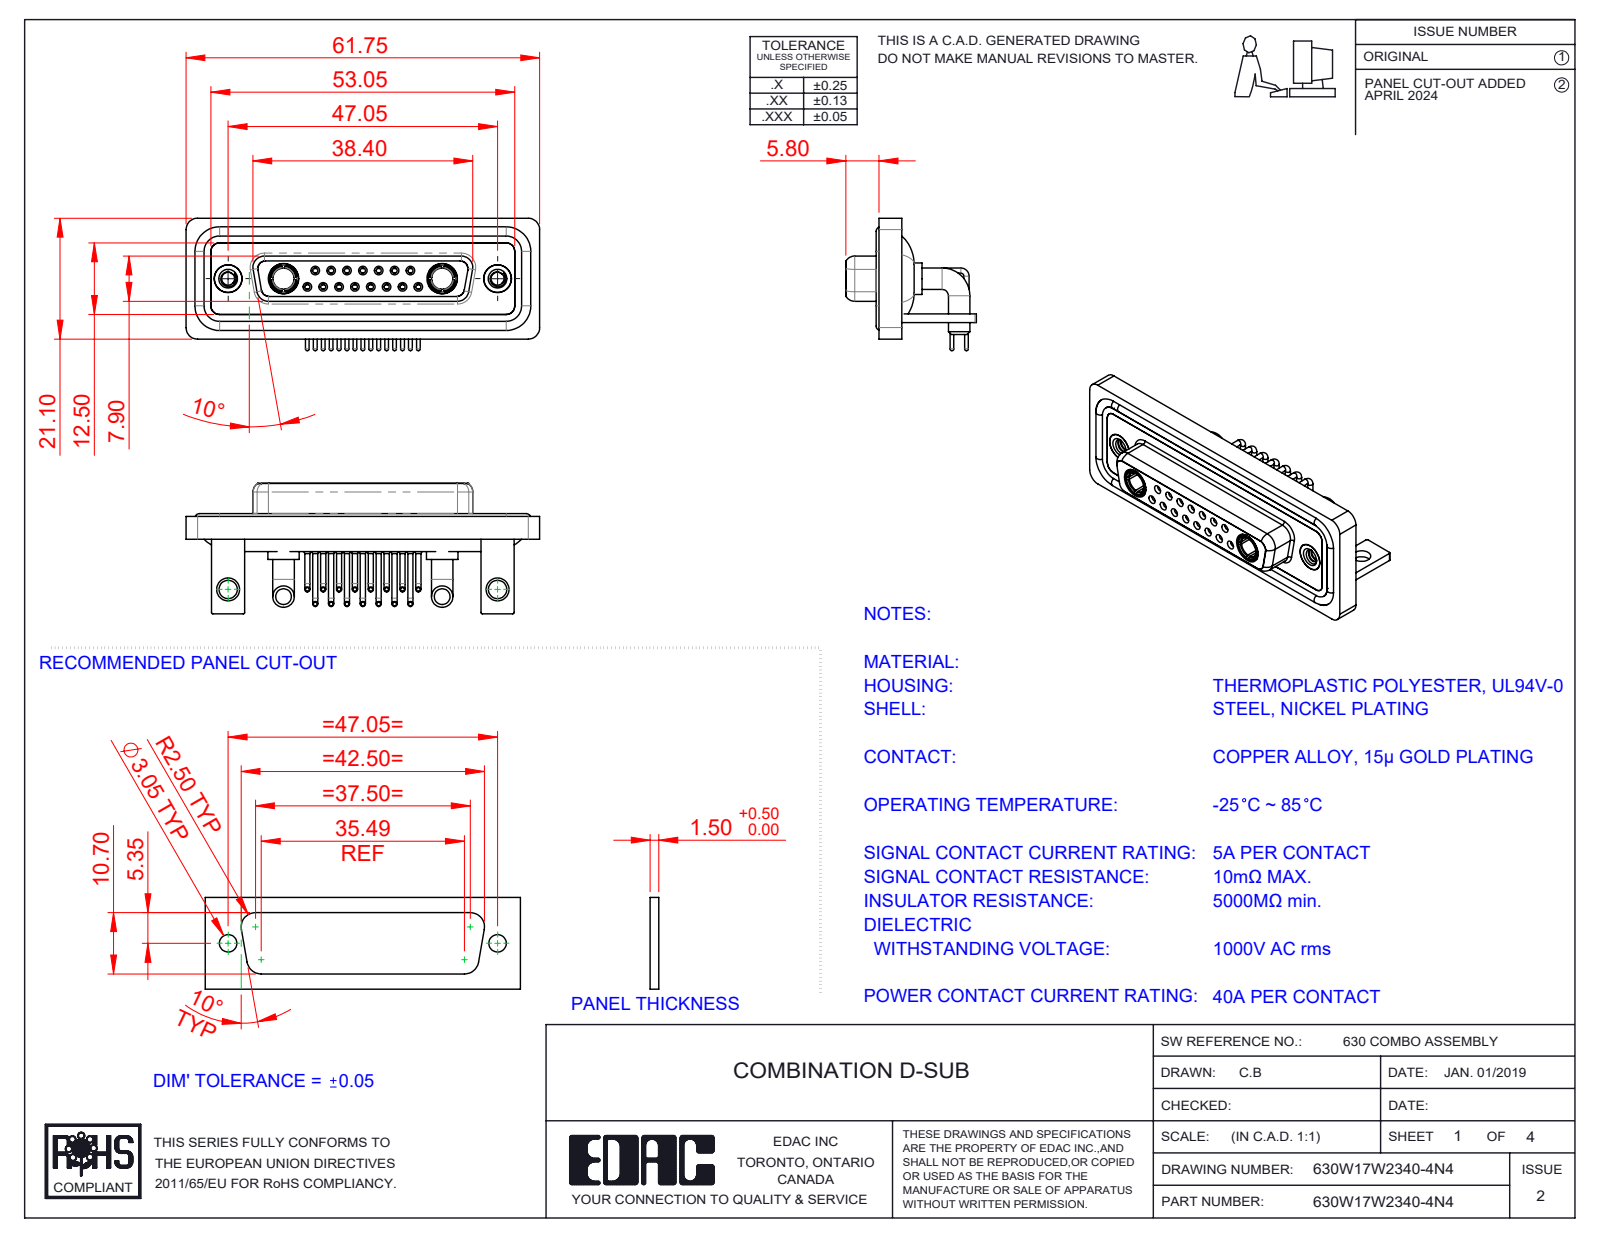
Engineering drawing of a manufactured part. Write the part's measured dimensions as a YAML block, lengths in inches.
part_name: "630Combo Housing_17W2; 630Combo Threaded Rivet_2; Power Socket_40A RA; 630Combo Stabilizer Bracket_50 Contacts (+6 more)"
step_written_by: "SolidWorks 2023 (CONFIG_CONTROL_DESIGN)"
units: inches
bodies: {solids: 28, faces: 1385, planar: 408, cylindrical: 607, other: 370}
overall_size: [2.431, 0.91, 0.898]
volume: 0.549
surface_area: 23.8
round_holes:
  - {diameter: 0.035, count: 15}
  - {diameter: 0.043, count: 15}
  - {diameter: 0.059, count: 15}
  - {diameter: 0.079, count: 15}
  - {diameter: 0.063, count: 8}
  - {diameter: 0.067, count: 7}
  - {diameter: 0.191, count: 4}
  - {diameter: 0.089, count: 2}
  - {diameter: 0.126, count: 2}
  - {diameter: 0.146, count: 2}
  - {diameter: 0.157, count: 2}
  - {diameter: 0.159, count: 2}
round_bosses_or_shafts:
  - {diameter: 0.035, count: 15}
  - {diameter: 0.026, count: 15}
  - {diameter: 0.063, count: 11}
  - {diameter: 0.148, count: 4}
  - {diameter: 0.217, count: 2}
  - {diameter: 0.205, count: 2}
  - {diameter: 0.195, count: 2}
  - {diameter: 0.195, count: 2}
partial_cylinders:
  - {radius: 0.079, count: 19}
  - {radius: 0.059, count: 18}
  - {radius: 0.01, count: 16}
  - {radius: 0.053, count: 8}
  - {radius: 0.063, count: 8}
  - {radius: 0.02, count: 5}
  - {radius: 0.024, count: 4}
  - {radius: 0.026, count: 4}
face_to_face_distances: [0.016, 0.071, 0.114, 0.146, 0.059, 0.161, 0.043, 0.055, 0.063, 0.122]
hole_center_spacings: [0.124, 0.109, 0.218, 0.327, 0.198, 0.295, 0.436, 0.198]
